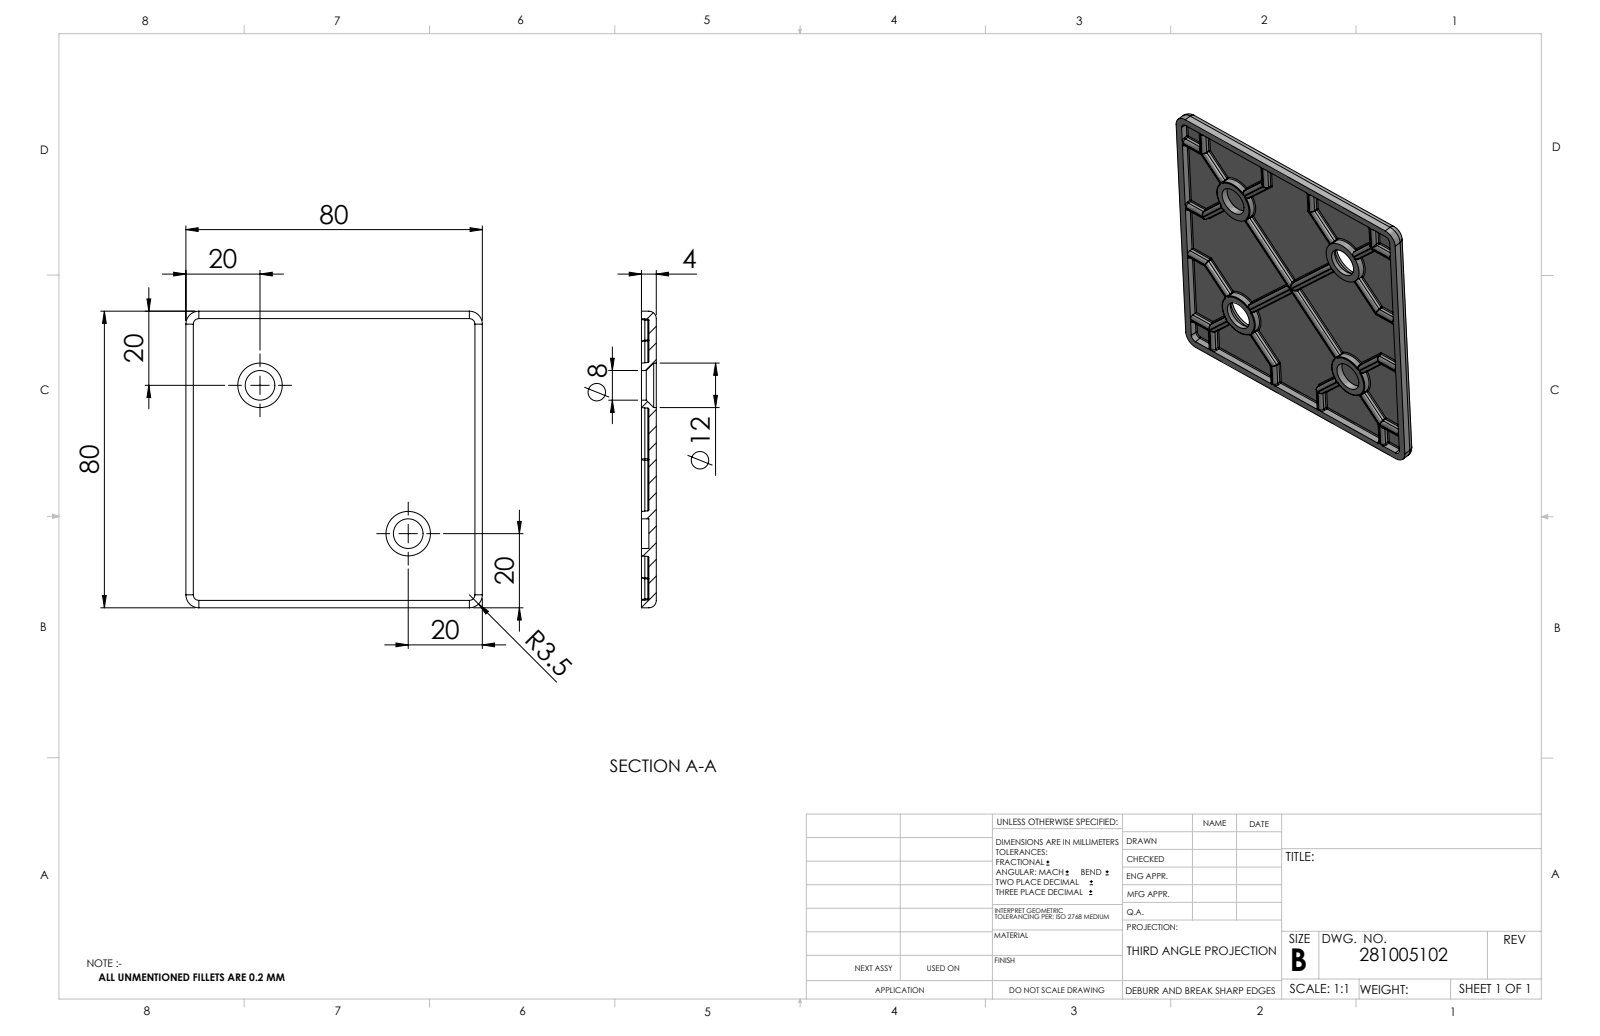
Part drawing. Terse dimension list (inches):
name: 281005102_c_1
written by: SolidWorks 2014 (CONFIG_CONTROL_DESIGN)
unit: in
bodies: 1 solid, 613 faces (108 planar, 223 cylindrical, 282 other)
size: 3.15 × 3.15 × 0.157
volume: 0.926 in³; area: 23.76 in²
holes: 4× ⌀0.315, 2× ⌀0.472
rounds: 102× R0.012, 28× R0.039, 4× R0.079, 4× R0.138
face distances: 0.079, 0.157, 3.15, 1.109, 2.217, 1.199, 0.885, 0.314, 0.66, 1.545
hole spacings: 1.575, 1.58, 2.227, 2.23
